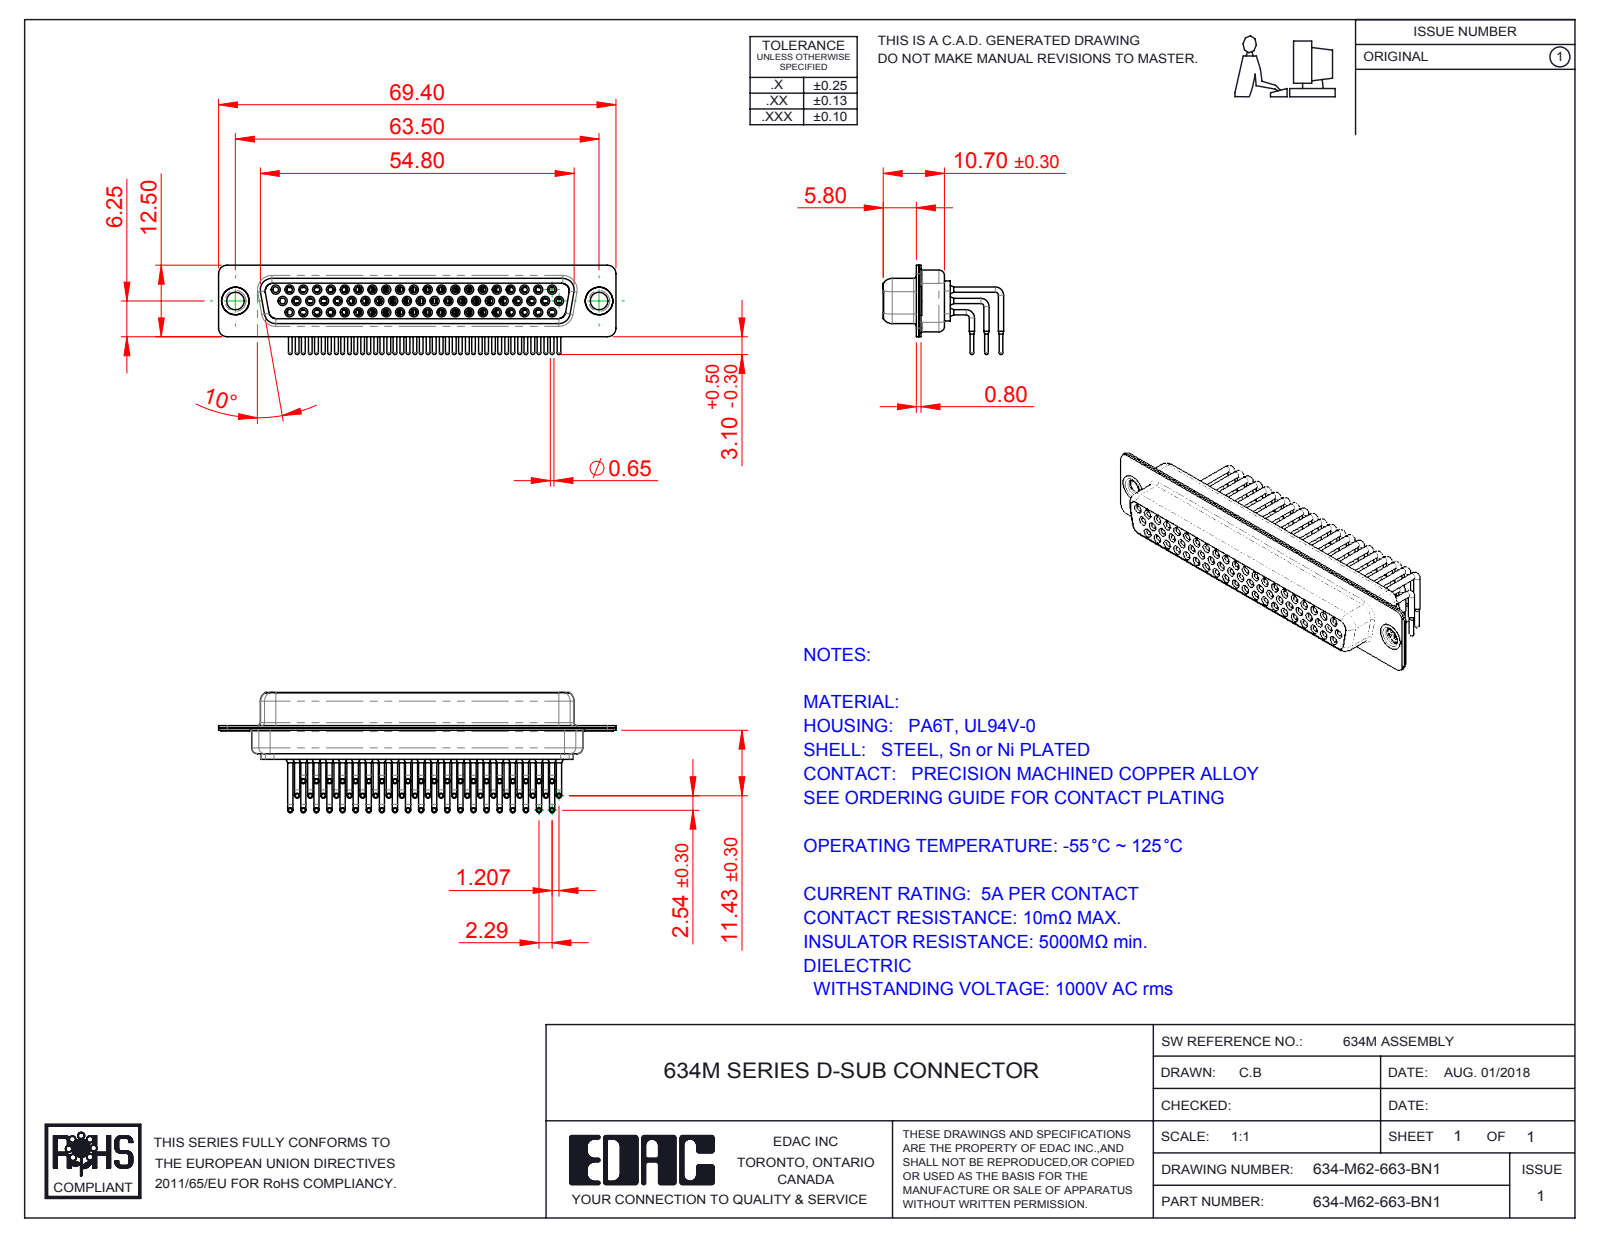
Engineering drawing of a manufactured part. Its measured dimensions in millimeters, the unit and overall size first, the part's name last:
Units: millimetres
Overall size (bounding box): 69.4 × 21.02 × 15.6
Round holes (diameter × count): ⌀1 ×62, ⌀1.1 ×62, ⌀1.7 ×62, ⌀1.8 ×62, ⌀2 ×62, ⌀3.05 ×2, ⌀4 ×2, ⌀4.8 ×2
Round bosses / shafts (diameter × count): ⌀0.9 ×124, ⌀1.6 ×62, ⌀1.5 ×62, ⌀0.65 ×62, ⌀2 ×56, ⌀5 ×2, ⌀4.9 ×2, ⌀3.55 ×2
Partial cylindrical surfaces — rounded edges, fillets, slot ends (radius × count): R1.5 ×16, R2 ×12, R1.35 ×8, R1.6 ×8, R0.25 ×4, R0.5 ×4, R0.6 ×4, R0.65 ×4
Main face-to-face distances: 0.4, 1.45, 8.95, 1.9, 8.5, 2.3, 6.2, 0.45, 7.05, 0.85
Hole centre spacings: 7.24, 2.32, 2.41, 9.65, 4.13, 4.83, 16.89, 14.48
Volume: 5 326 mm³ · Surface area: 17 717 mm²
Bodies: 67 solids, 3539 faces (997 planar, 1547 cylindrical, 995 other)
Part name (STEP PRODUCT): 634M Thru Hole Rivet; 634M Contact Row 2; 634M Housing_62 Contacts; 634M Shell Front_62 Contacts (+4 more)
STEP written by: SolidWorks 2016 (CONFIG_CONTROL_DESIGN)
